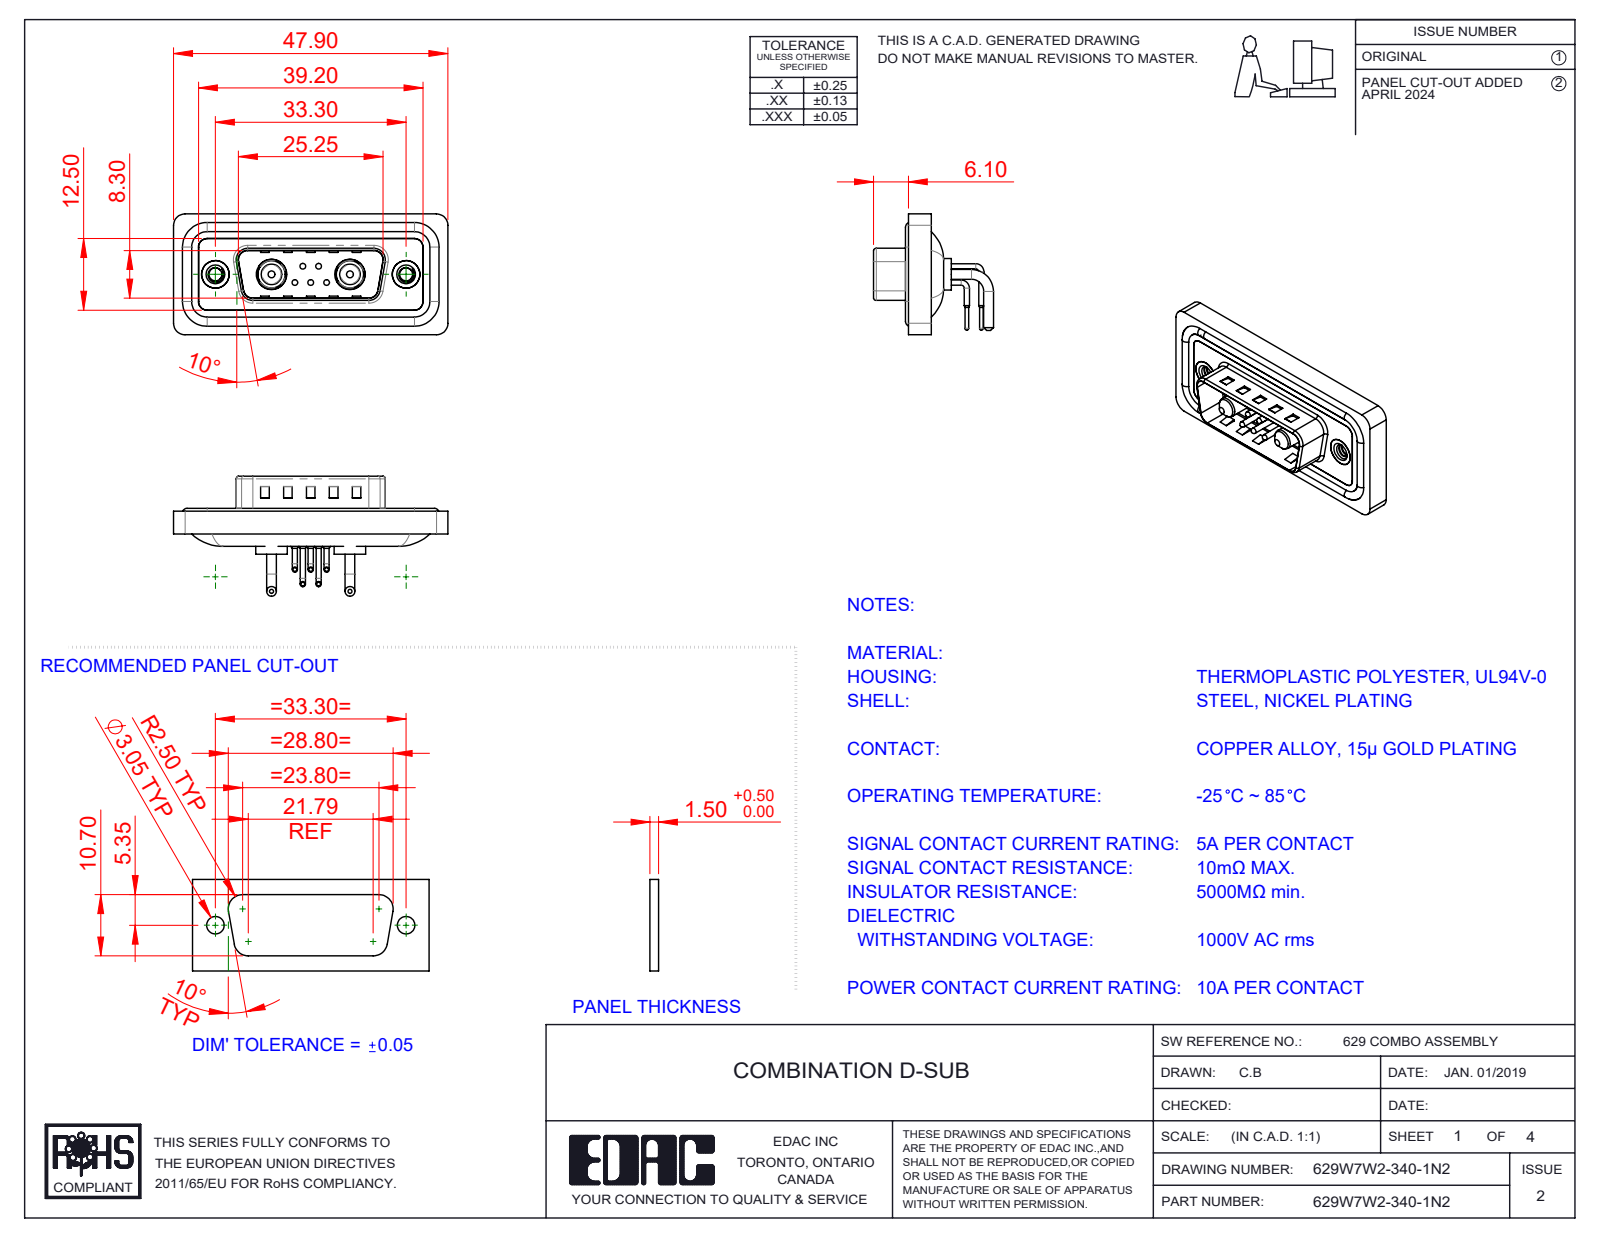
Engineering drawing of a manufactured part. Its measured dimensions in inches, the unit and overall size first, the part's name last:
Units: inches
Overall size (bounding box): 1.886 × 0.831 × 0.825
Round holes (diameter × count): ⌀0.03 ×5, ⌀0.063 ×5, ⌀0.079 ×5, ⌀0.089 ×2, ⌀0.157 ×2, ⌀0.189 ×2, ⌀0.191 ×2, ⌀0.197 ×2, ⌀0.209 ×2
Round bosses / shafts (diameter × count): ⌀0.035 ×10, ⌀0.059 ×5, ⌀0.039 ×5, ⌀0.026 ×5, ⌀0.067 ×4, ⌀0.063 ×4, ⌀0.217 ×2, ⌀0.205 ×2
Partial cylindrical surfaces — rounded edges, fillets, slot ends (radius × count): R0.079 ×20, R0.059 ×18, R0.02 ×8, R0.063 ×8, R0.04 ×5, R0.01 ×4, R0.024 ×4, R0.026 ×4
Main face-to-face distances: 0.016, 0.114, 0.031, 0.043, 0.083, 0.063, 0.098, 0.122, 0.177, 0.161
Hole centre spacings: 0.124, 0.109, 0.386, 0.925, 0.17, 0.17, 0.198, 0.198
Volume: 0.34 in³ · Surface area: 14.01 in²
Bodies: 16 solids, 1083 faces (517 planar, 406 cylindrical, 160 other)
Part name (STEP PRODUCT): Power Pin_10A RA; 629Combo Contact Row 1; 629W7W2-340-1N2; 629Combo Shell Rear_15 Contacts (+5 more)
STEP written by: SolidWorks 2023 (CONFIG_CONTROL_DESIGN)
